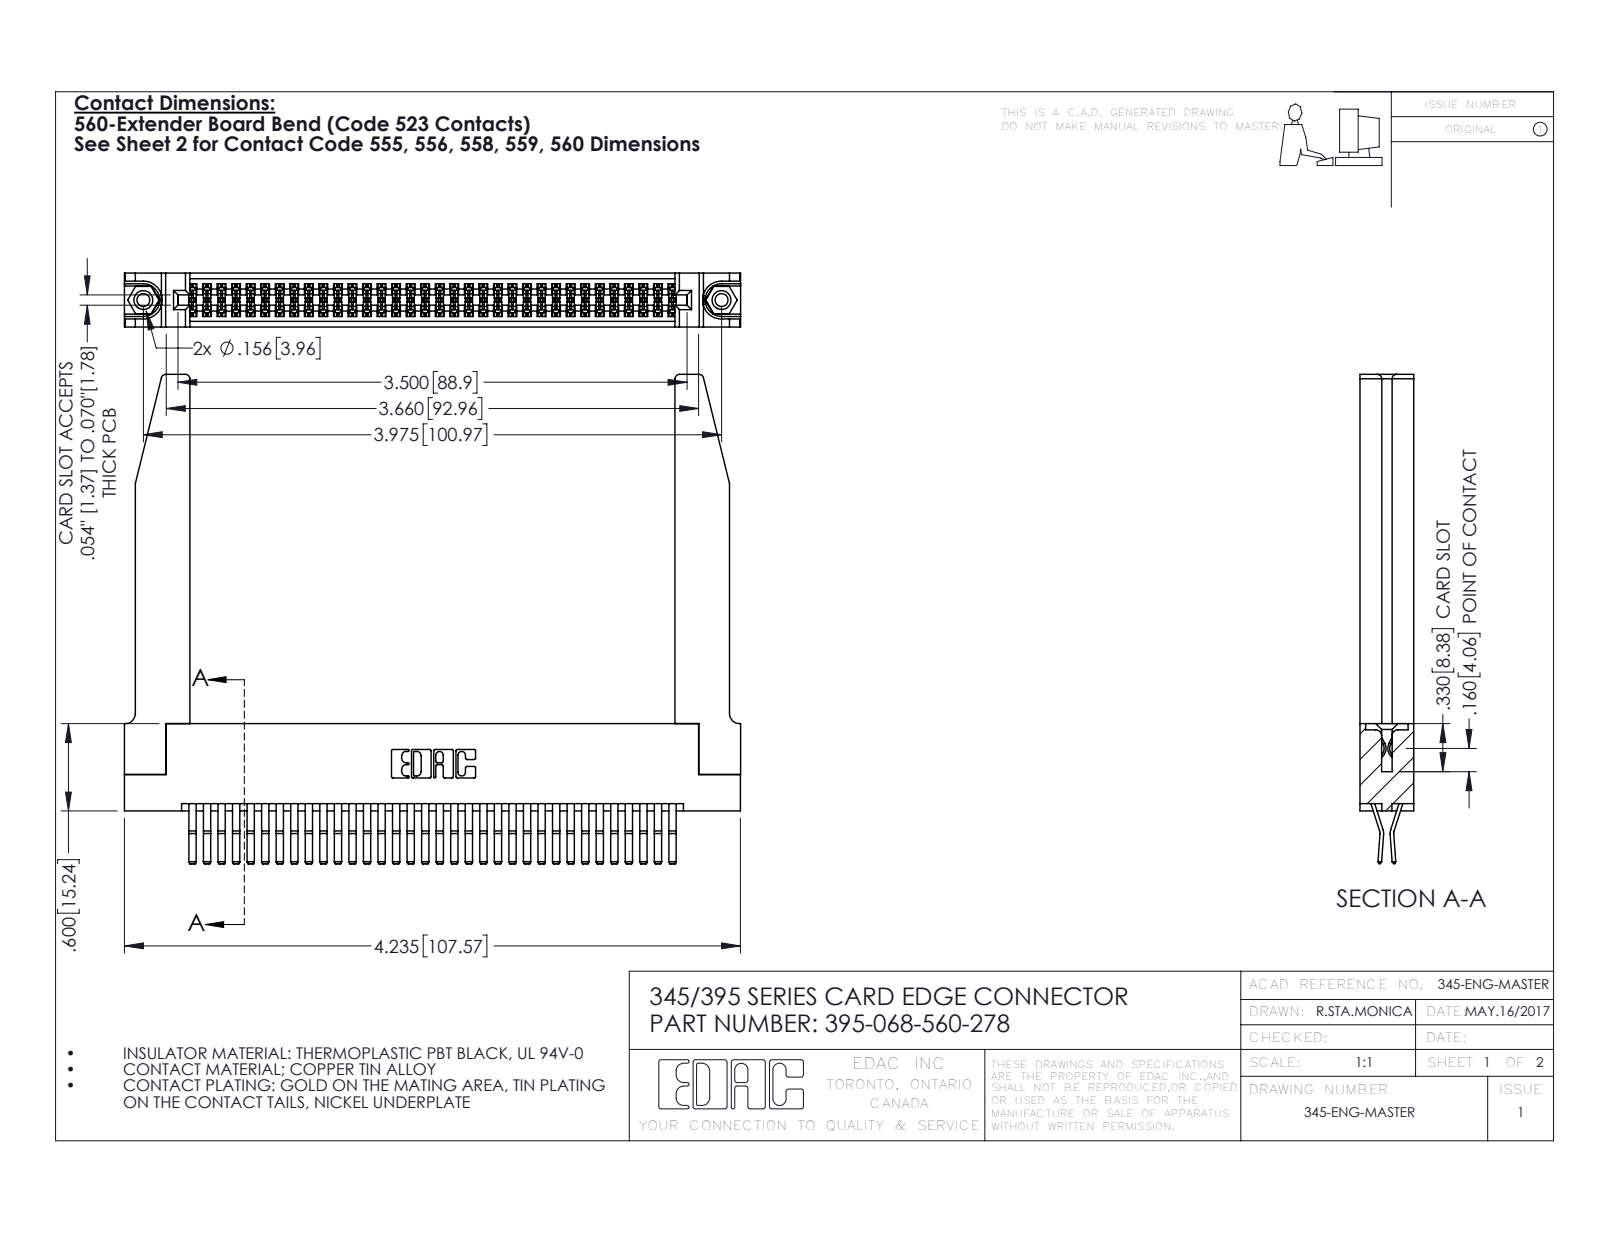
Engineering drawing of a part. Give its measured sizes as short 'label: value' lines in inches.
name: 345-250-001_345-250-001-102; 395-068-560-278; 345-220-078_345-220-078; 345 Part_Flush Mounting Lugs - 0.156 Dia-TH (+1 more)
written by: SolidWorks 2016 (CONFIG_CONTROL_DESIGN)
unit: in
bodies: 73 solids, 3896 faces (2466 planar, 1378 cylindrical, 52 other)
size: 4.236 × 3.362 × 0.37
volume: 1.135 in³; area: 36.93 in²
holes: 2× ⌀0.089, 2× ⌀0.125, 2× ⌀0.156, 1× ⌀0.064
bosses: 2× ⌀0.155
rounds: 102× R0.006, 22× R0.01, 8× R0.03, 6× R0.007, 6× R0.031, 3× R0.026, 2× R0.01, 2× R0.014
face distances: 0.37, 0.072, 0.298, 0.025, 0.2, 0.098, 0.272, 0.225, 0.15, 0.148
hole spacings: 0.27, 3.74, 3.975
